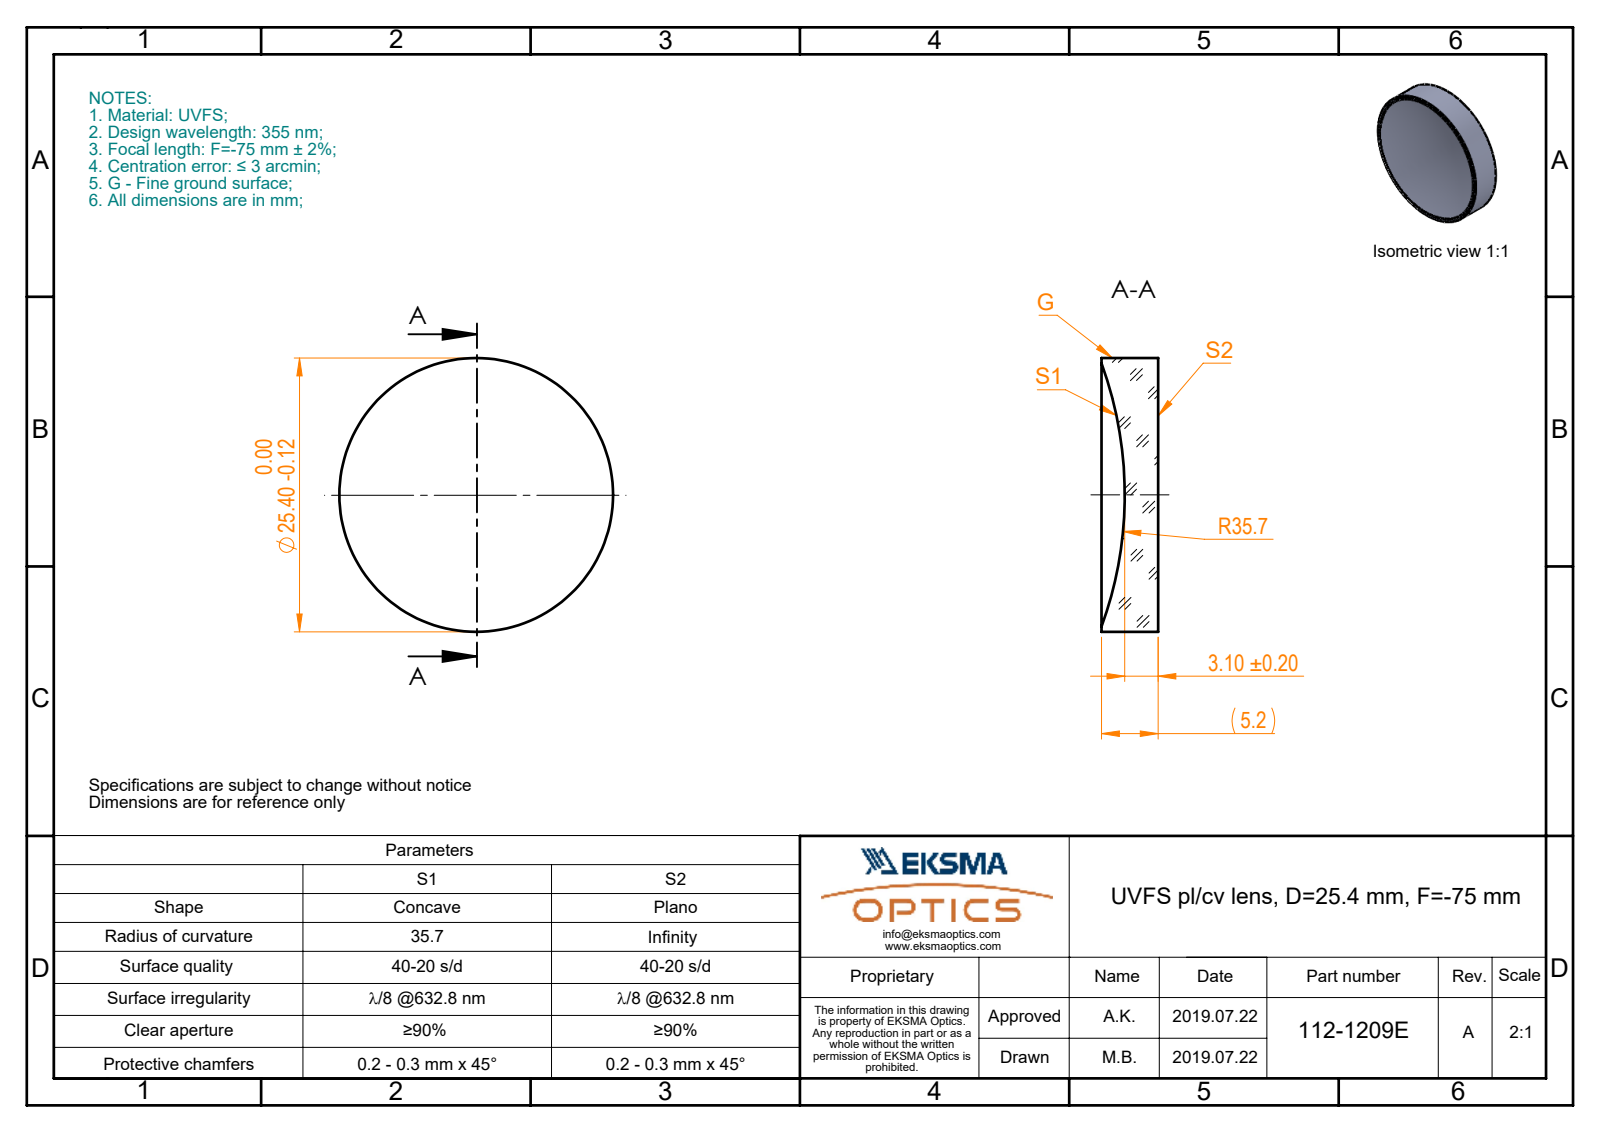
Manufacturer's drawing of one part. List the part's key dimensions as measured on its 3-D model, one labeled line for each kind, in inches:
Part name (STEP PRODUCT): 112-1209E UVFS pl-cv 12.7 F-75
STEP written by: SolidWorks 2017 (CONFIG_CONTROL_DESIGN)
Units: inches
Bodies: 1 solid, 6 faces (2 planar, 2 cylindrical, 2 other)
Overall size (bounding box): 1 × 1 × 0.207
Volume: 0.131 in³ · Surface area: 2.243 in²
Round bosses / shafts (diameter × count): ⌀1 ×1
Main face-to-face distances: 0.207
